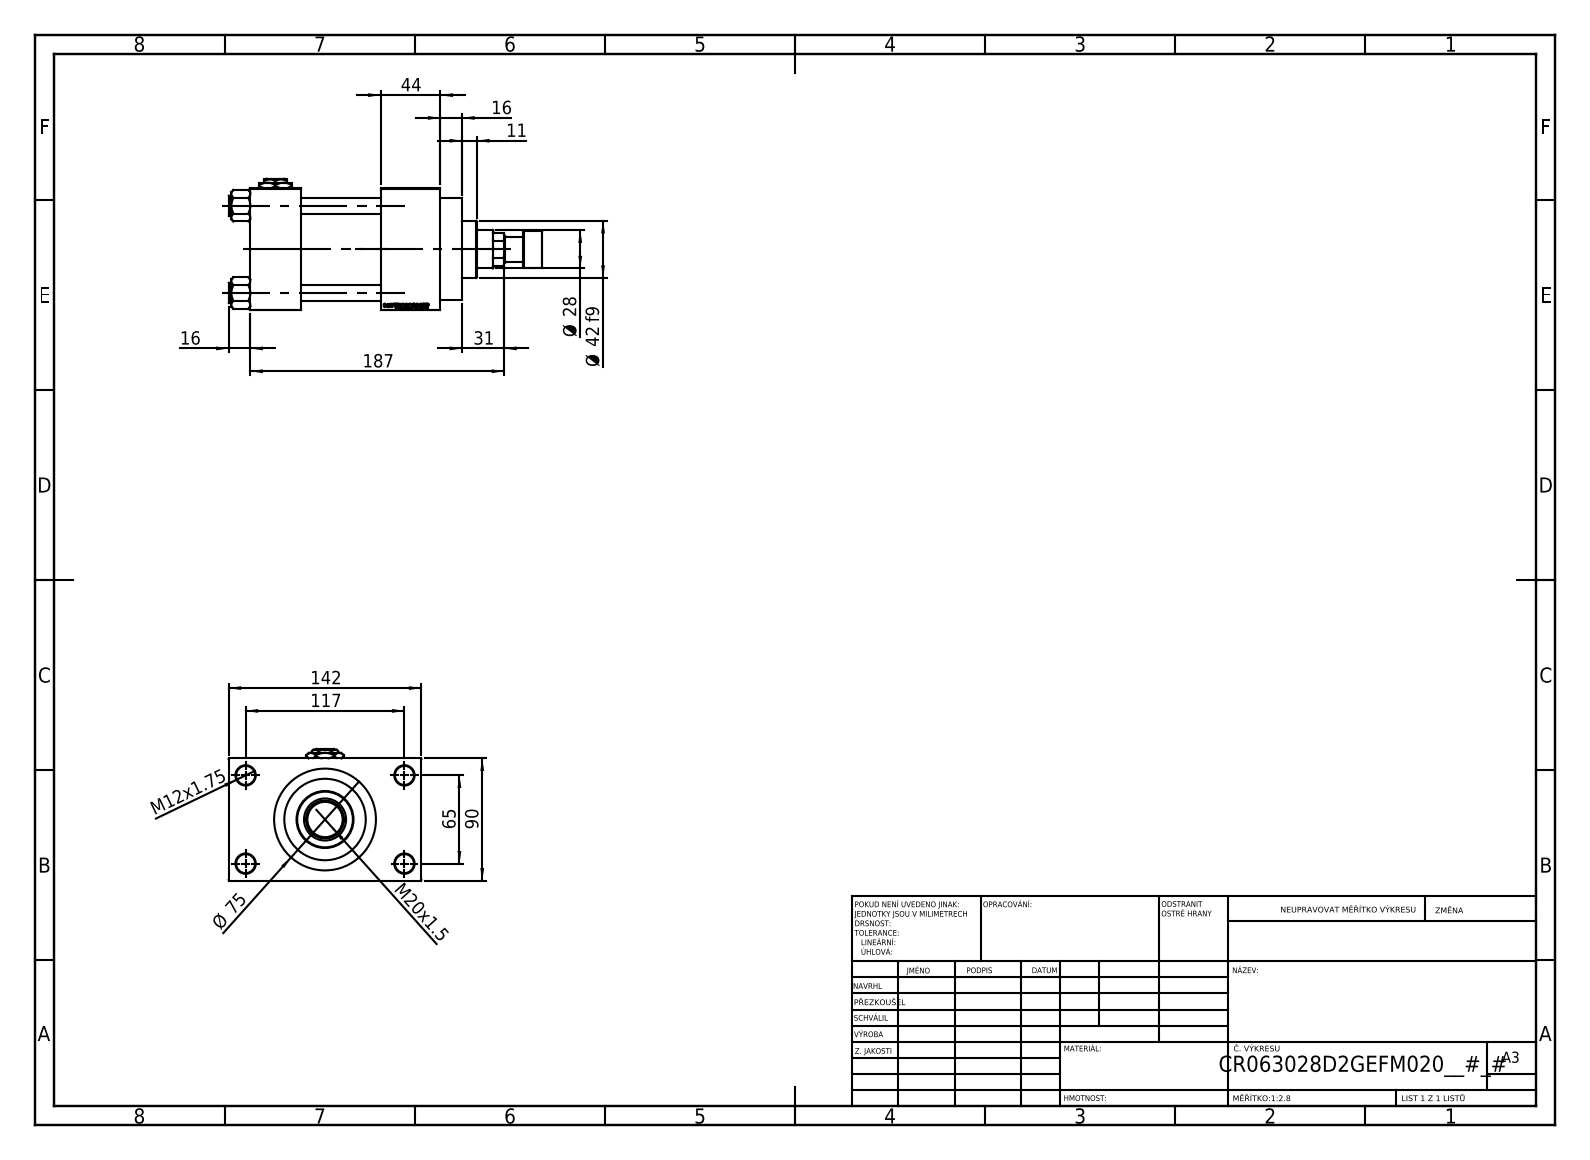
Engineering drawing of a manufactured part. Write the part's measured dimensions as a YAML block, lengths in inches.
part_name: "NUT_M5_D; V215CR_D_TYCINKA; Zatka_pro_OIL_PORT; V215CR_D_Body (+3 more)"
step_written_by: "SolidWorks 2019 (CONFIG_CONTROL_DESIGN)"
units: inches
bodies: {solids: 13, faces: 1171, planar: 525, cylindrical: 100, other: 546}
overall_size: [9.094, 5.591, 3.819]
volume: 67.98
surface_area: 317.2
round_holes:
  - {diameter: 0.472, count: 4}
  - {diameter: 0.551, count: 4}
  - {diameter: 0.276, count: 2}
  - {diameter: 0.825, count: 2}
  - {diameter: 1.181, count: 2}
  - {diameter: 0.728, count: 1}
  - {diameter: 1.102, count: 1}
  - {diameter: 1.22, count: 1}
  - {diameter: 1.969, count: 1}
  - {diameter: 2.362, count: 1}
  - {diameter: 2.48, count: 1}
round_bosses_or_shafts:
  - {diameter: 0.591, count: 4}
  - {diameter: 2.953, count: 1}
  - {diameter: 2.717, count: 1}
  - {diameter: 1.654, count: 1}
  - {diameter: 1.063, count: 1}
  - {diameter: 0.709, count: 1}
face_to_face_distances: [3.543, 2.323, 1.457, 3.78, 5.512, 4.055, 1.732, 1.024, 4.567, 5.591]
hole_center_spacings: [1.037, 1.79, 2.531, 2.635, 2.748, 3.569, 4.383, 2.559]
